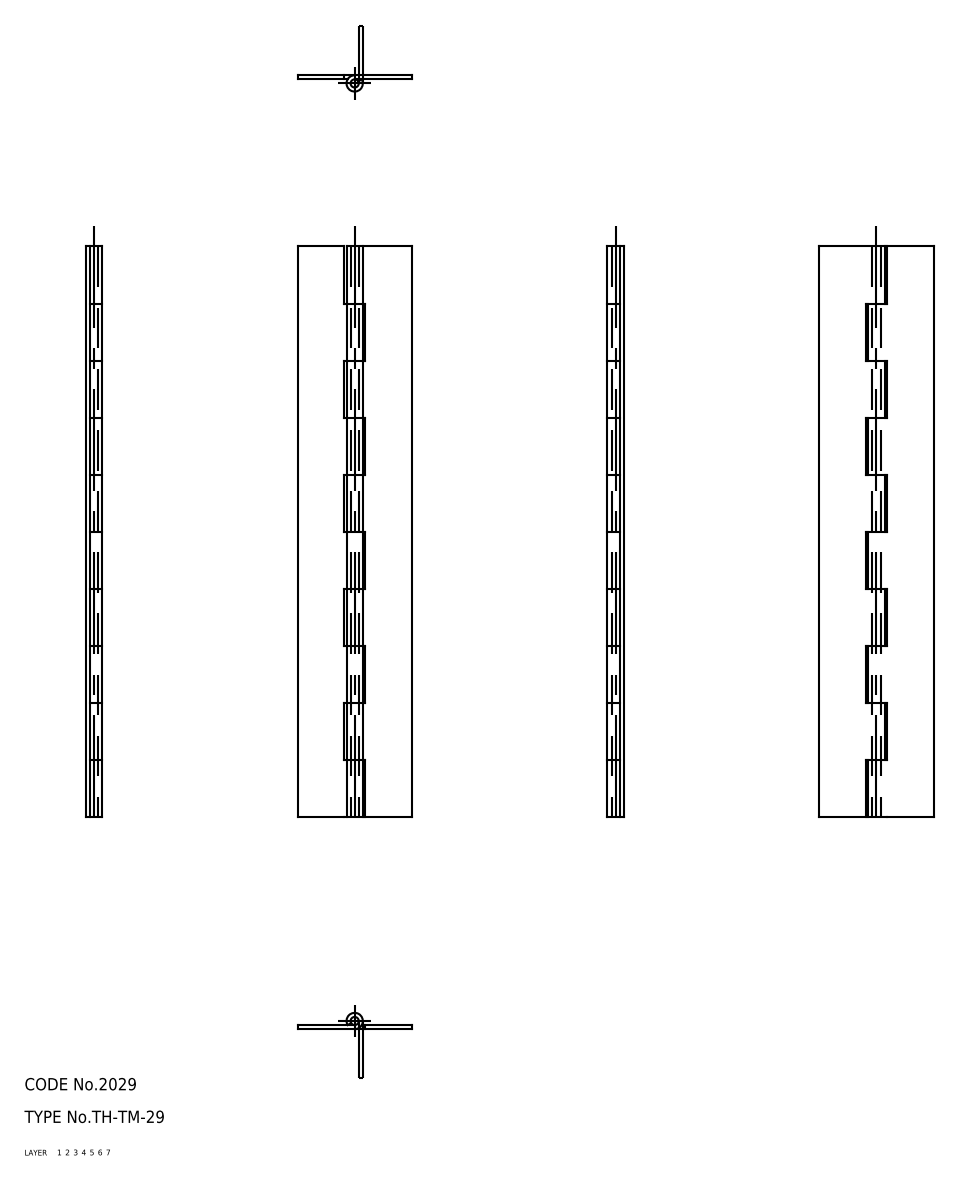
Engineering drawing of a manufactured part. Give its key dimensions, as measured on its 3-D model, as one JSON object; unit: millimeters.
{"part_name": "hinge piece_B; hinge piece_A; shaft; TH_TM_29_22434_36", "step_written_by": "CADfix (AUTOMOTIVE_DESIGN)", "units": "millimeters", "bodies": {"solids": 3, "faces": 72, "planar": 0, "cylindrical": 0, "other": 72}, "overall_size": [140, 28, 4], "volume_mm3": 5090, "surface_area_mm2": 11000}
